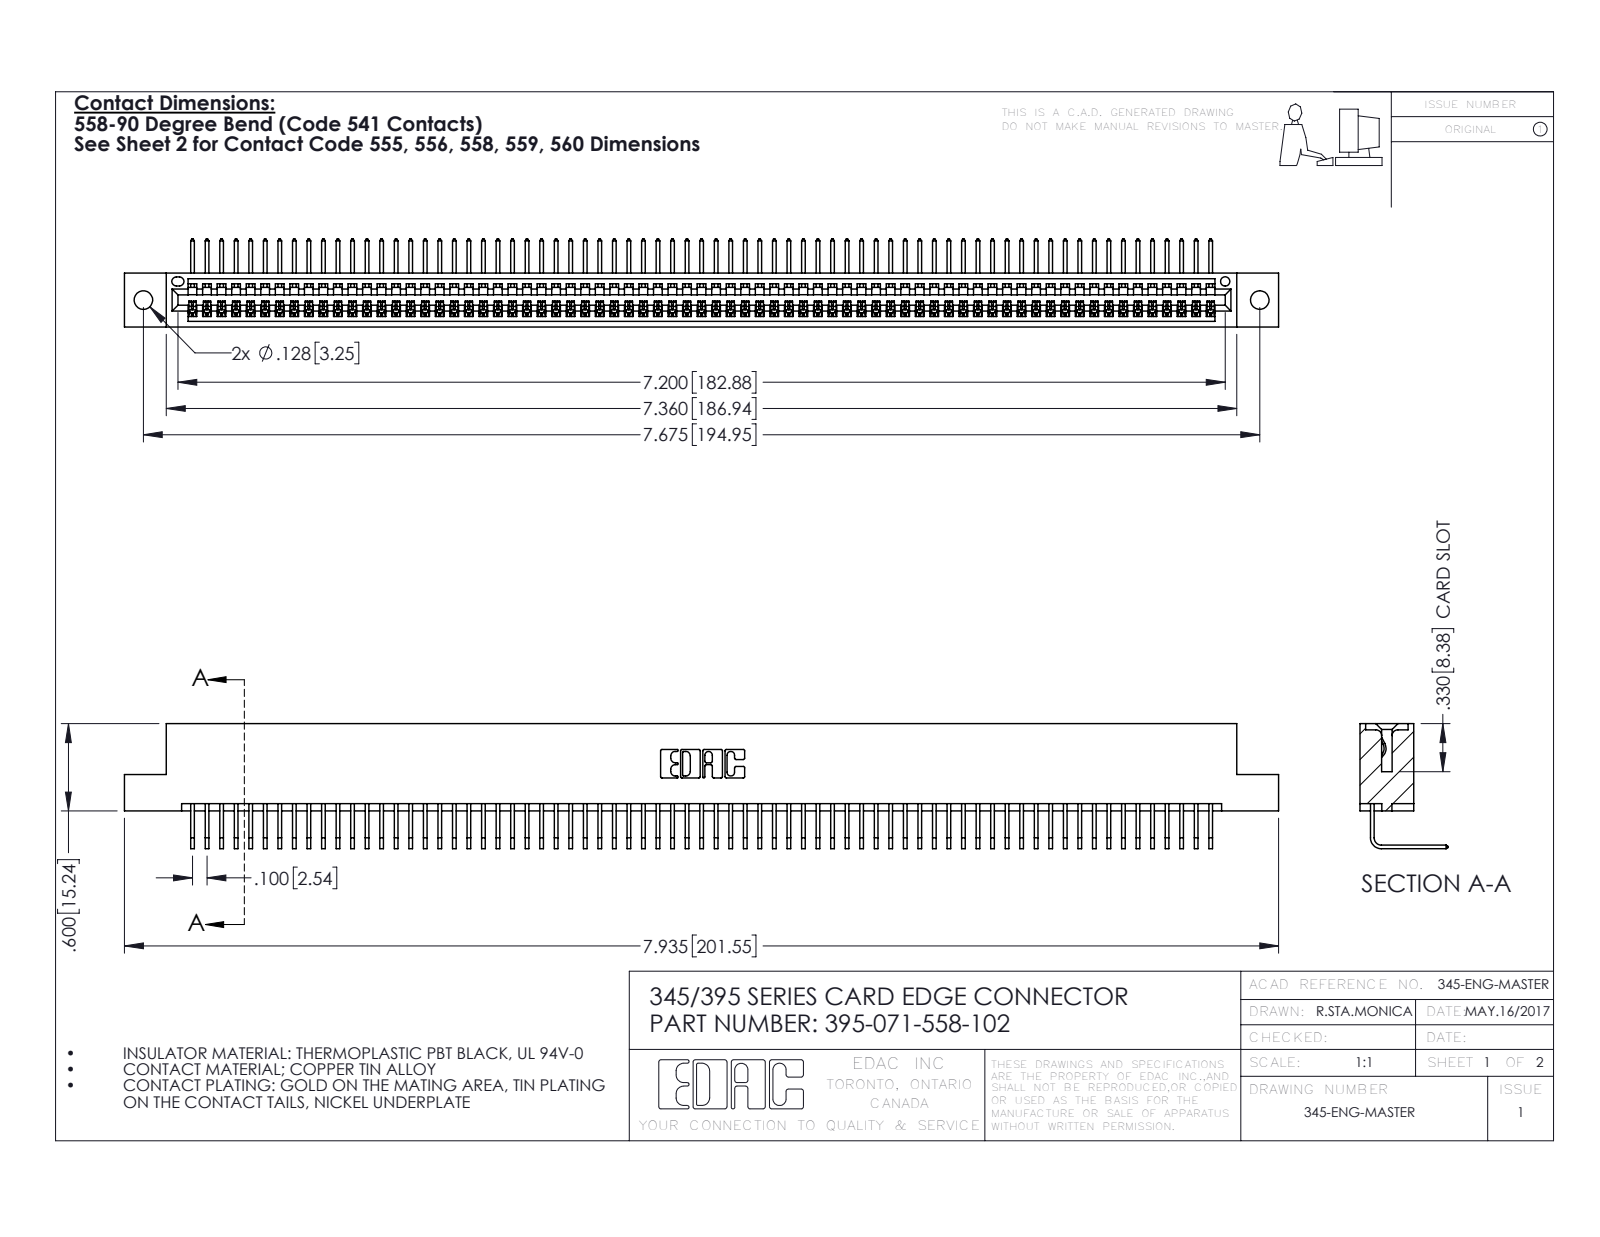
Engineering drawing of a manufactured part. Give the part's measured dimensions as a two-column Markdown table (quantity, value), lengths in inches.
| quantity | value |
| --- | --- |
| part name | 345 Part_Flush Mounting Lugs - 0.128 Dia; 345-292-001_558 Tail - 2; 395-071-558-102 |
| STEP written by | SolidWorks 2016 (CONFIG_CONTROL_DESIGN) |
| units | inches |
| bodies | 72 solids, 4386 faces (3062 planar, 1324 cylindrical, 0 other) |
| overall size | 7.935 × 0.859 × 0.605 |
| volume | 1.195 in³ |
| surface area | 42.68 in² |
| round holes (diameter × count) | 0.128 × 2, 0.064 × 1 |
| partial cylindrical surfaces (radius × count) | 0.006 × 142, 0.01 × 22, 0.007 × 6, 0.031 × 6, 0.026 × 3, 0.031 × 2, 0.04 × 2, 0.014 × 1 |
| main face-to-face distances | 0.298, 0.072, 0.37, 0.2, 0.098, 0.272, 0.025, 0.225, 0.149, 0.072 |
| hole center spacings | 0.27, 7.439, 7.675 |
